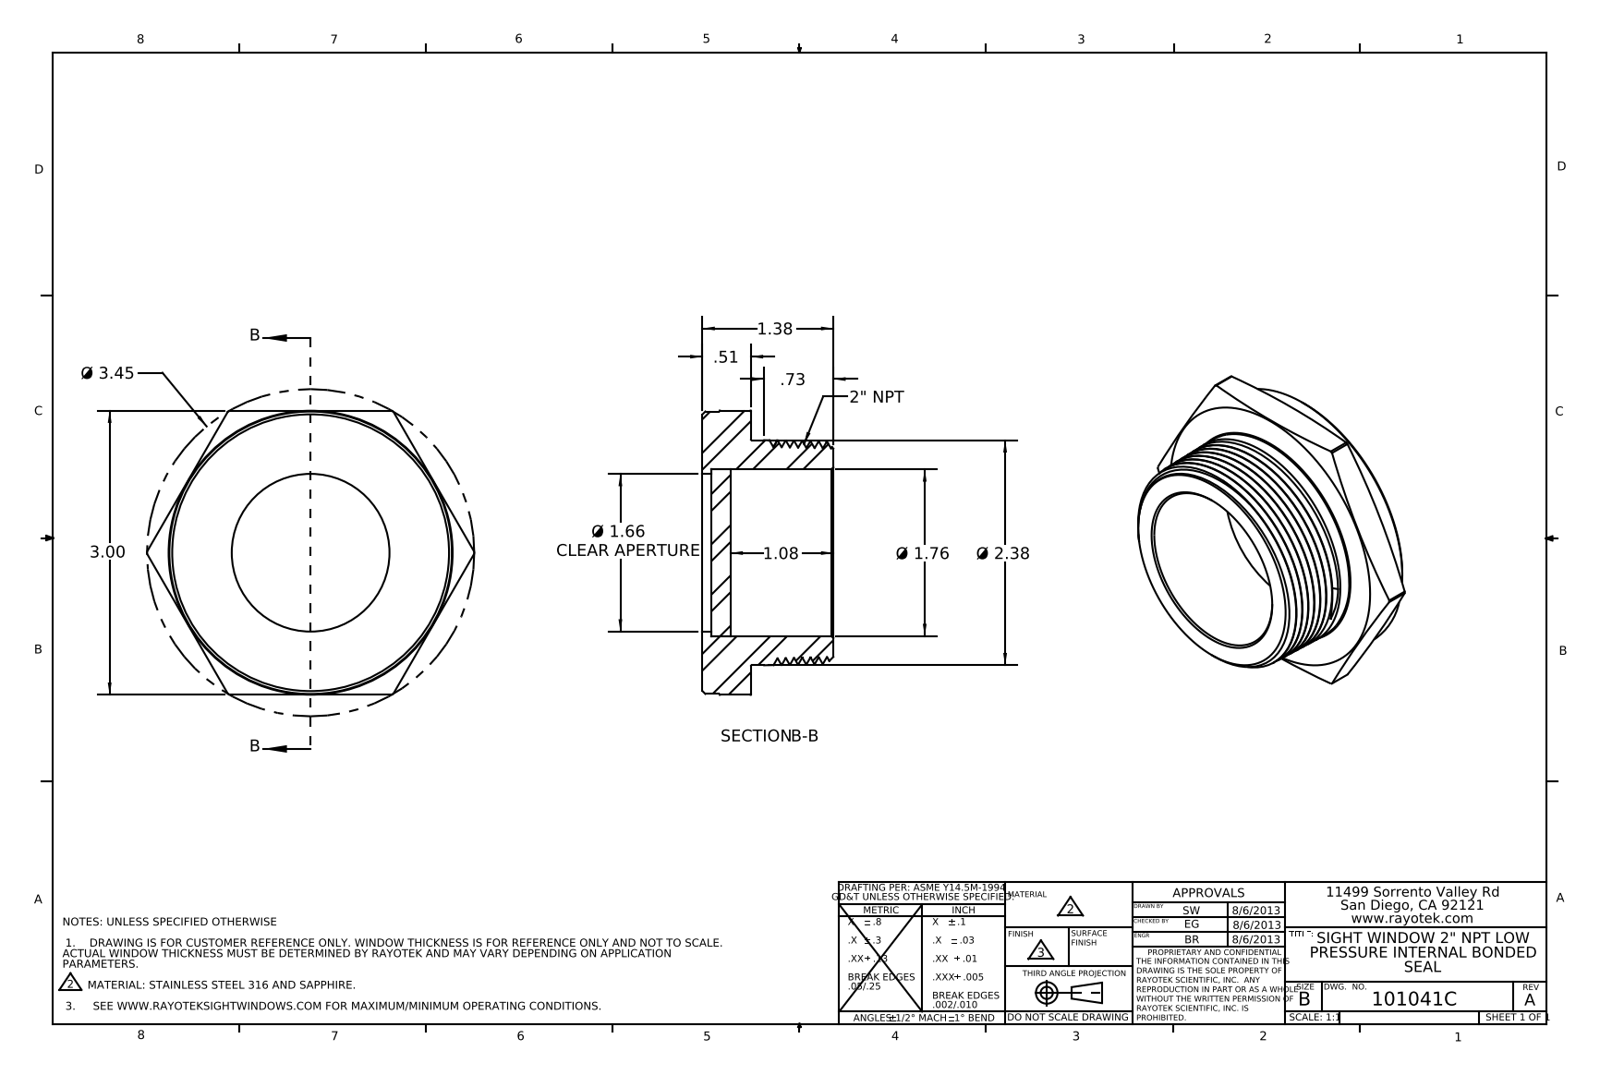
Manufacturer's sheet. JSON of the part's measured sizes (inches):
{"part_name": "403041", "step_written_by": "SolidWorks 2012 (AUTOMOTIVE_DESIGN)", "units": "inches", "bodies": {"solids": 2, "faces": 65, "planar": 15, "cylindrical": 17, "other": 33}, "overall_size": [3.452, 3, 1.38], "volume_in3": 4.59, "surface_area_in2": 39.09, "round_holes": [[1.664, 1], [1.76, 1]], "round_bosses_or_shafts": [[2.98, 1], [2.375, 1]], "partial_cylinders_radius": [[1.726, 1]], "face_to_face_distances": [0.096, 0.51, 0.414, 0.296, 0.2, 0.214, 3, 1.38, 1.284, 1.084]}
